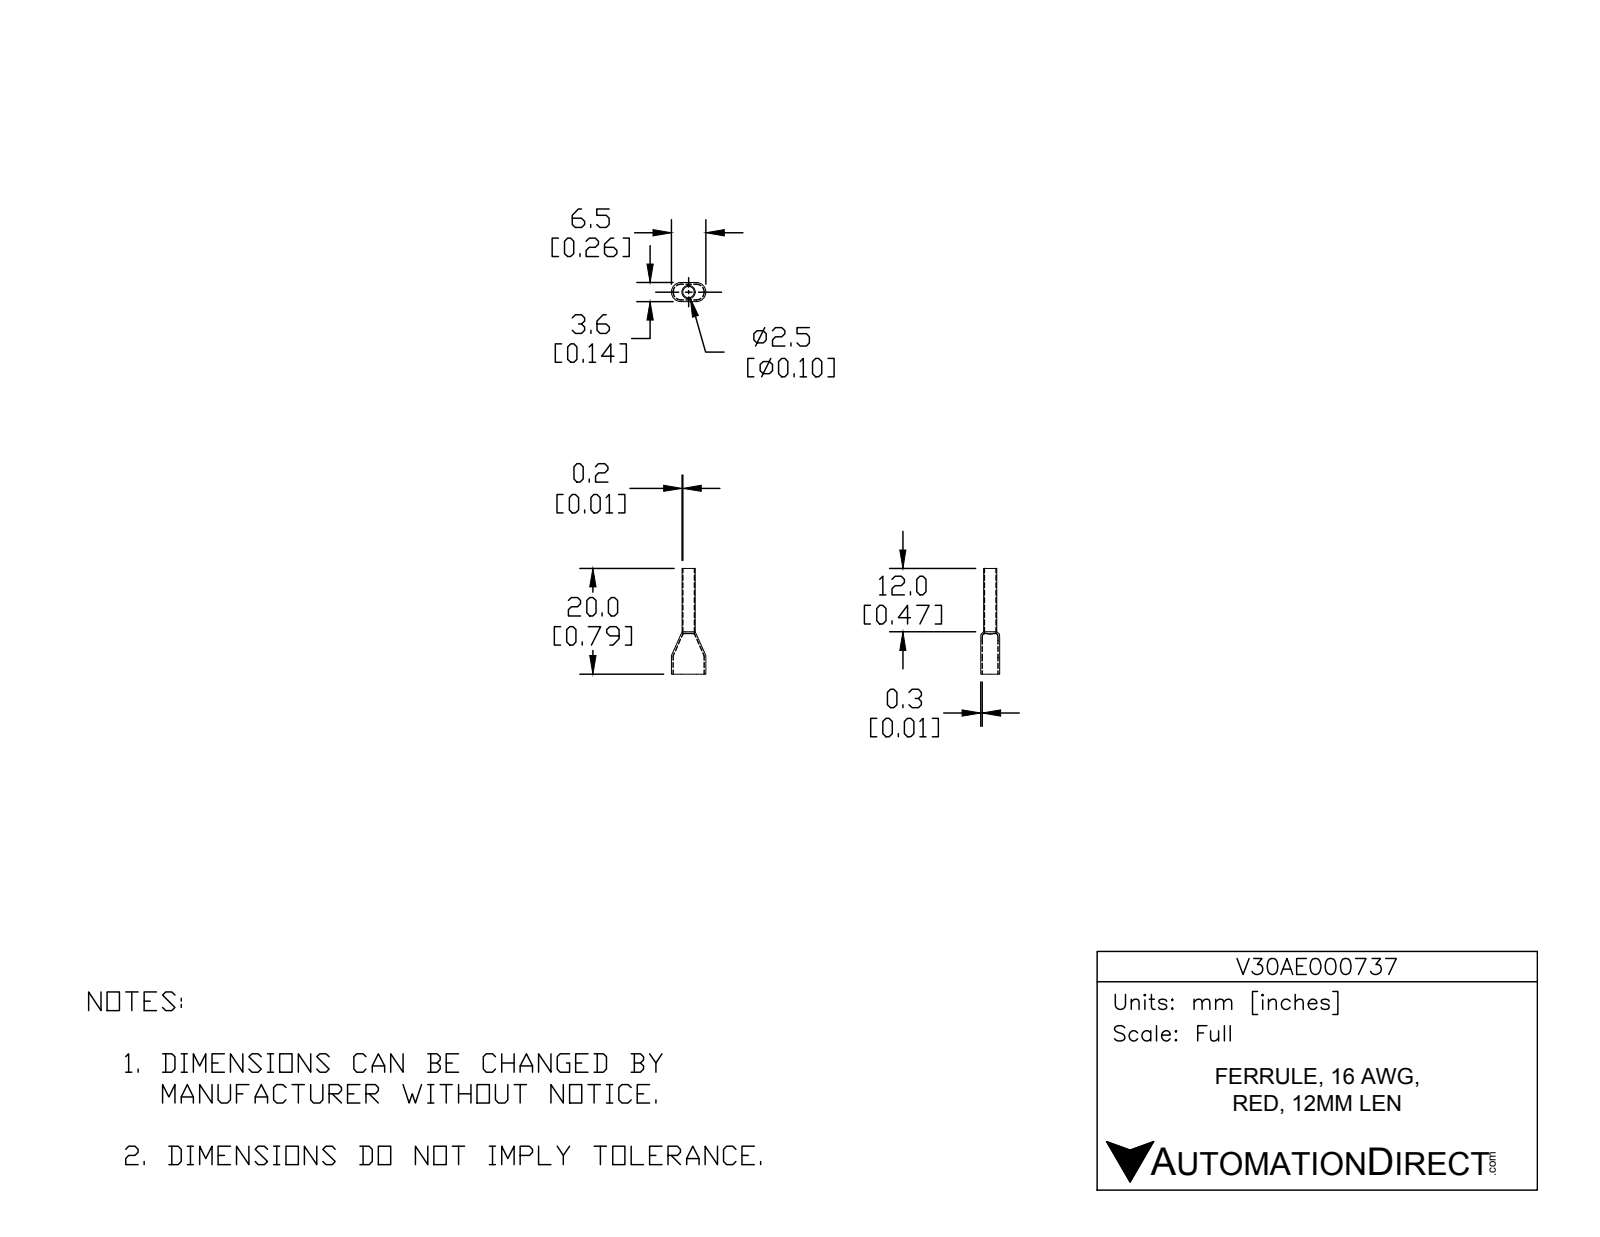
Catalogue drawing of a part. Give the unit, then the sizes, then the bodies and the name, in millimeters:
Units: millimetres
Overall size (bounding box): 20 × 6.5 × 3.6
Round holes (diameter × count): ⌀2.2 ×1
Round bosses / shafts (diameter × count): ⌀2.5 ×1
Partial cylindrical surfaces — rounded edges, fillets, slot ends (radius × count): R1.5 ×5, R1.8 ×5
Main face-to-face distances: 3.3, 3.6, 3, 8, 20, 12, 7.7, 12.3
Volume: 47 mm³ · Surface area: 412 mm²
Bodies: 2 solids, 36 faces (14 planar, 22 cylindrical, 0 other)
Part name (STEP PRODUCT): V30AE000737
STEP written by: SolidWorks 2017 (AUTOMOTIVE_DESIGN)
